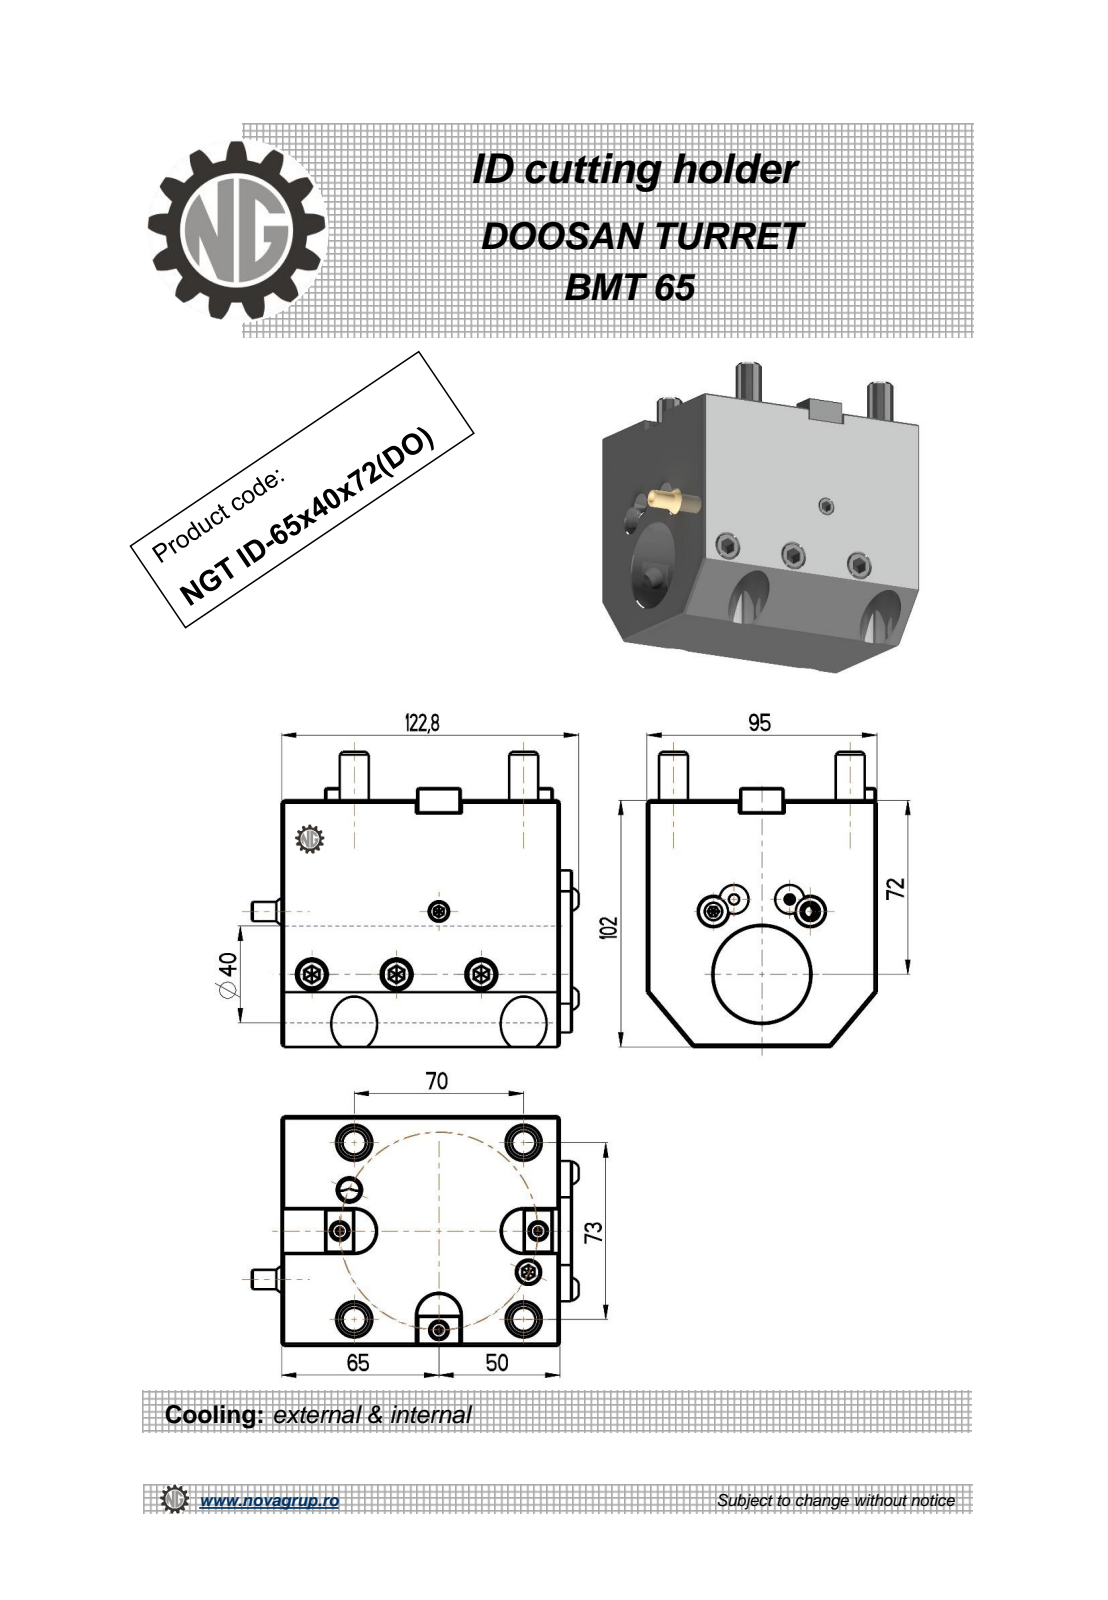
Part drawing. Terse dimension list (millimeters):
name: NGT_ID_65_40_72_DO
written by: PRO/ENGINEER BY PARAMETRIC TECHNOLOGY CORPORATION, 2010280 (CONFIG_CONTROL_DESIGN)
unit: mm
bodies: 1 solid, 373 faces (203 planar, 73 cylindrical, 97 other)
size: 135.09 × 122 × 95
volume: 937 403 mm³; area: 85 958 mm²
holes: 3× ⌀10.2, 1× ⌀5, 1× ⌀8.5, 1× ⌀40
bosses: 4× ⌀12, 1× ⌀8
rounds: 36× R0.61, 6× R0.51, 3× R9
face distances: 95, 102, 115, 5, 120, 97, 20, 38, 18, 107
hole spacings: 35, 32.8, 70
